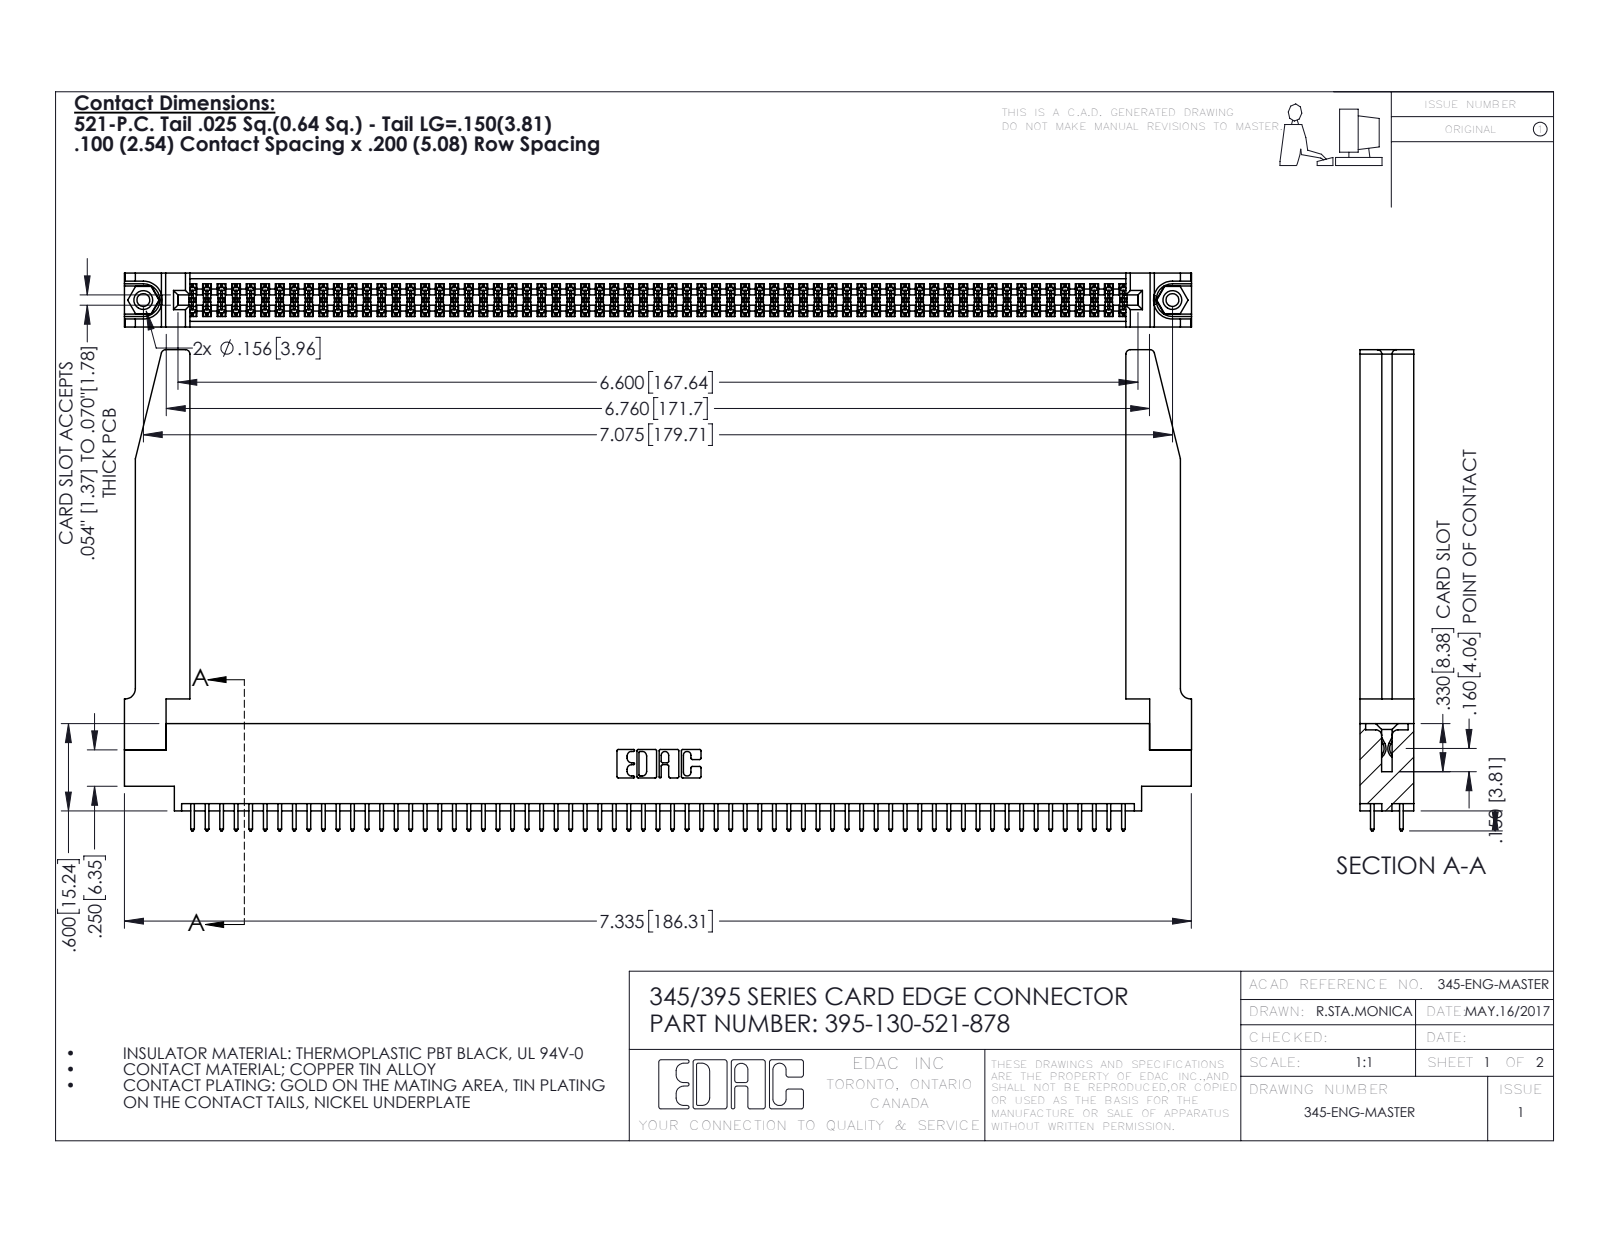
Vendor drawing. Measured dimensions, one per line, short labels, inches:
name: 345-292-001_345-293-121; 345 Part_0.170 Offset - 0.156 Dia-TH; 345-250-001_345-250-001-102; 345-220-078_345-220-078 (+1 more)
written by: SolidWorks 2016 (CONFIG_CONTROL_DESIGN)
unit: in
bodies: 135 solids, 6864 faces (4516 planar, 2296 cylindrical, 52 other)
size: 7.336 × 3.307 × 0.37
volume: 1.582 in³; area: 52.56 in²
holes: 2× ⌀0.089, 2× ⌀0.125, 2× ⌀0.156, 1× ⌀0.064
bosses: 2× ⌀0.155
rounds: 195× R0.006, 130× R0.01, 22× R0.01, 8× R0.03, 6× R0.007, 6× R0.031, 3× R0.026, 2× R0.014
face distances: 0.072, 0.298, 0.37, 0.098, 0.272, 0.025, 0.2, 0.225, 0.175, 0.148
hole spacings: 0.27, 6.839, 7.075
